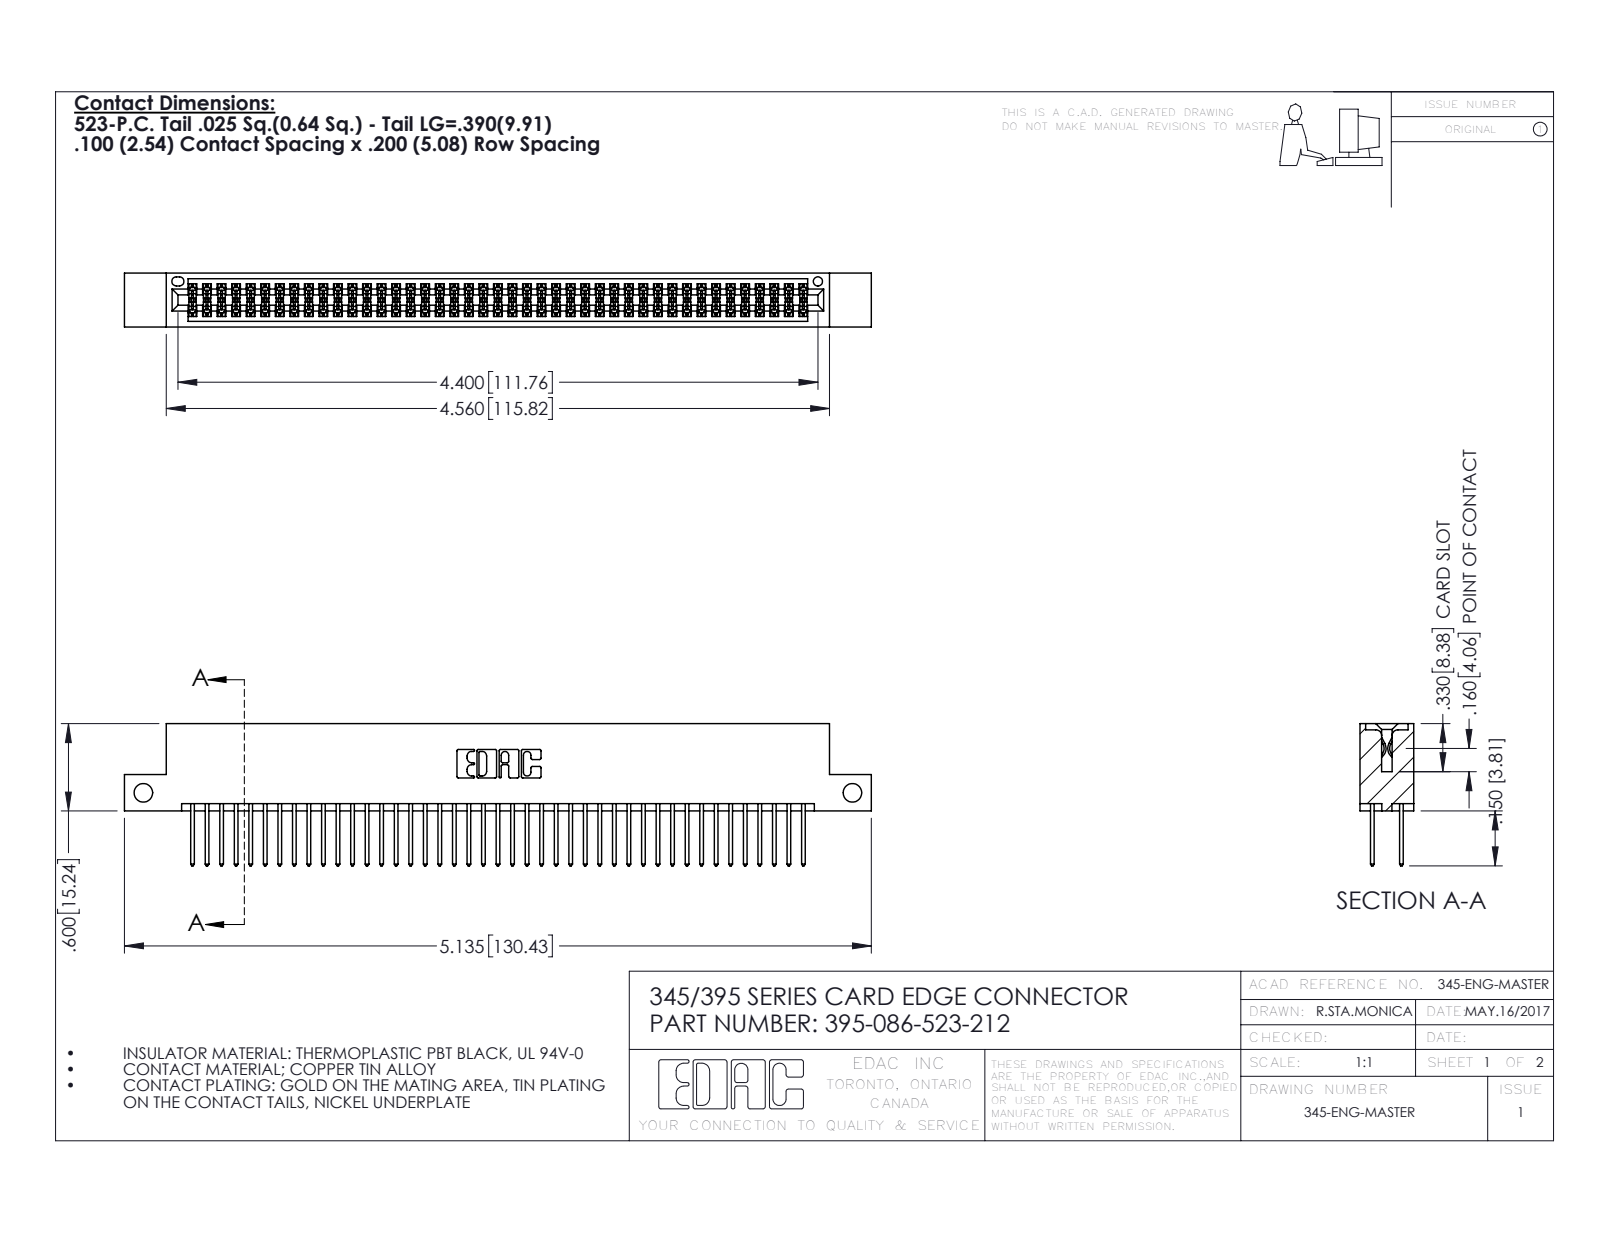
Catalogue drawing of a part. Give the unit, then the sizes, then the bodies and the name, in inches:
Units: inches
Overall size (bounding box): 5.135 × 0.977 × 0.37
Round holes (diameter × count): ⌀0.128 ×2, ⌀0.064 ×1
Partial cylindrical surfaces — rounded edges, fillets, slot ends (radius × count): R0.006 ×129, R0.01 ×86, R0.01 ×22, R0.007 ×6, R0.031 ×6, R0.026 ×3, R0.014 ×2, R0.019 ×2
Main face-to-face distances: 0.298, 0.072, 0.2, 0.098, 0.272, 0.025, 0.37, 0.225, 0.175, 0.149
Hole centre spacings: 4.875
Volume: 0.779 in³ · Surface area: 30.3 in²
Bodies: 87 solids, 4426 faces (2918 planar, 1508 cylindrical, 0 other)
Part name (STEP PRODUCT): 395-086-523-212; 345-292-001_345-293-123; 345 Part_Flush Mounting Lugs - Side Mount
STEP written by: SolidWorks 2016 (CONFIG_CONTROL_DESIGN)
